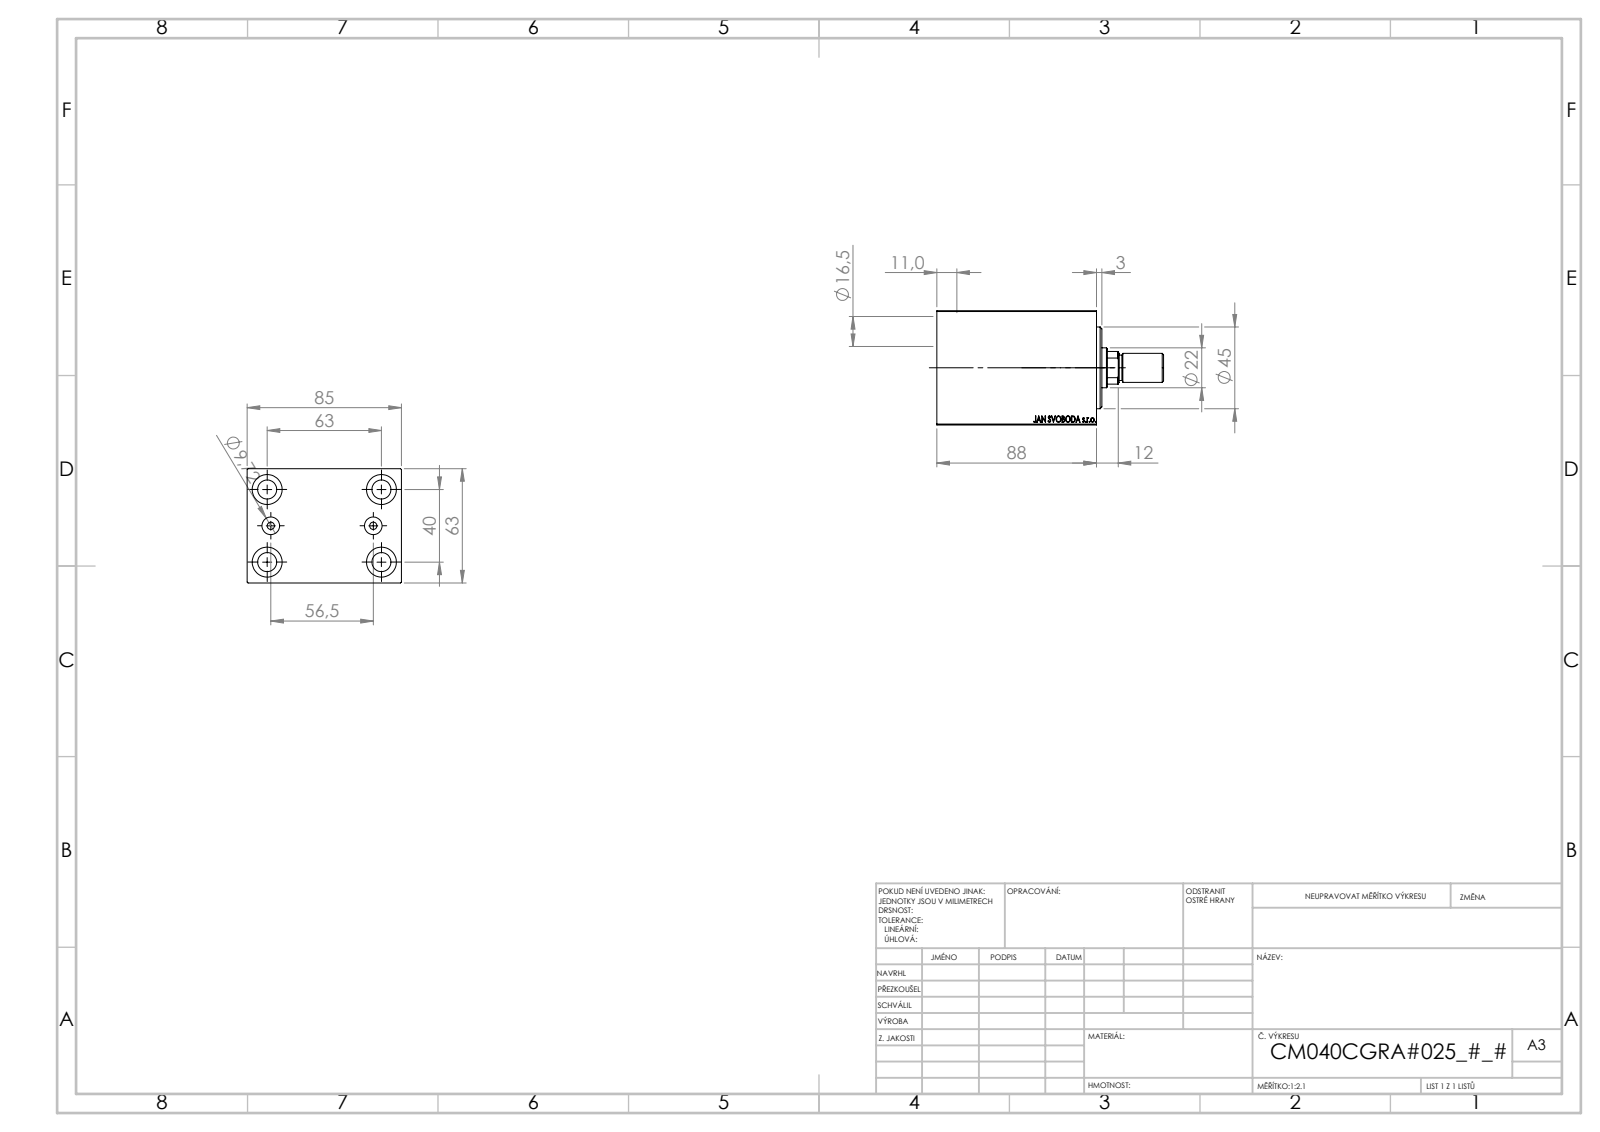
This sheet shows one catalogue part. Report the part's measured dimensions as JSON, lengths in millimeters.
{"part_name": "V450CM_C_Body; V450CM_C_VCP; V450CM_VC_B; V450CM_MALE_METRIC", "step_written_by": "SolidWorks 2019 (CONFIG_CONTROL_DESIGN)", "units": "millimeters", "bodies": {"solids": 4, "faces": 872, "planar": 412, "cylindrical": 60, "other": 400}, "overall_size": [125, 85, 63], "volume_mm3": 414084, "surface_area_mm2": 80112, "round_holes": [[10.5, 4], [16.5, 4], [4, 2], [9.72, 2], [12.5, 1], [22, 1], [25.5, 1], [40, 1], [42, 1], [45, 1]], "round_bosses_or_shafts": [[16, 1], [14, 1]], "partial_cylinders_radius": [[10.5, 1]], "face_to_face_distances": [63, 85, 12, 76, 88, 40, 1, 64, 11, 37], "hole_center_spacings": [37.31, 20.1, 20.5, 40, 61.82, 63, 64.2, 74.63]}
